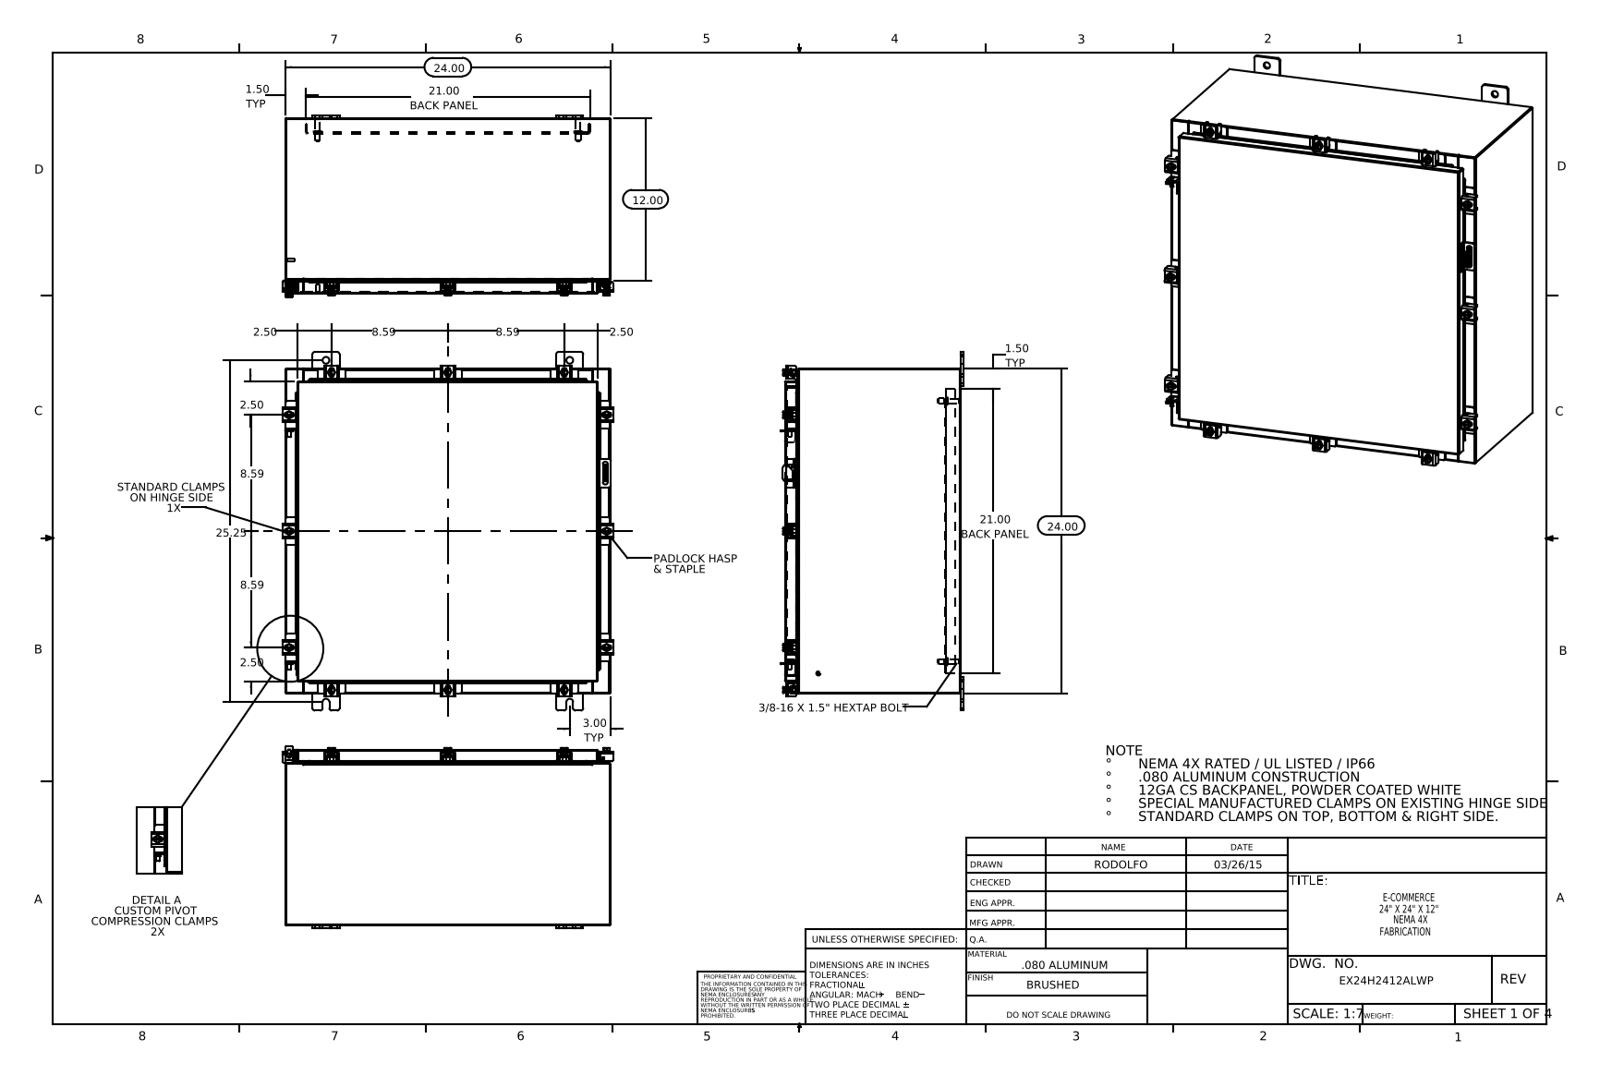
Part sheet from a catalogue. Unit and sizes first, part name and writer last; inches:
Units: inches
Overall size (bounding box): 26.5 × 24.421 × 13.453
Round holes (diameter × count): ⌀0.213 ×12, ⌀0.26 ×12, ⌀0.5 ×8, ⌀0.125 ×1, ⌀0.25 ×1
Round bosses / shafts (diameter × count): ⌀0.5 ×12, ⌀0.25 ×12, ⌀0.399 ×10, ⌀0.625 ×4, ⌀0.375 ×4, ⌀0.33 ×4, ⌀0.315 ×2, ⌀0.236 ×2
Partial cylindrical surfaces — rounded edges, fillets, slot ends (radius × count): R0.06 ×54, R0.013 ×24, R0.141 ×24, R0.19 ×24, R0.088 ×22, R0.12 ×22, R0.09 ×18, R0.05 ×17
Main face-to-face distances: 0.075, 23.925, 12.9, 23.85, 24, 12.975, 12.826, 0.104, 1, 1.075
Hole centre spacings: 20.559, 2.34, 18.34, 21.376, 23.451, 4.429, 8.593, 8.595
Volume: 245 in³ · Surface area: 6 171 in²
Bodies: 81 solids, 2018 faces (1075 planar, 783 cylindrical, 160 other)
Part name (STEP PRODUCT): EX24H2412ALWP Clamp Bracket; Quarter-20 CD Stud; ATEX CLAMP HINGE BRAKET; EX24H2412ALWP Top (+8 more)
STEP written by: SolidWorks 2014 (CONFIG_CONTROL_DESIGN)
